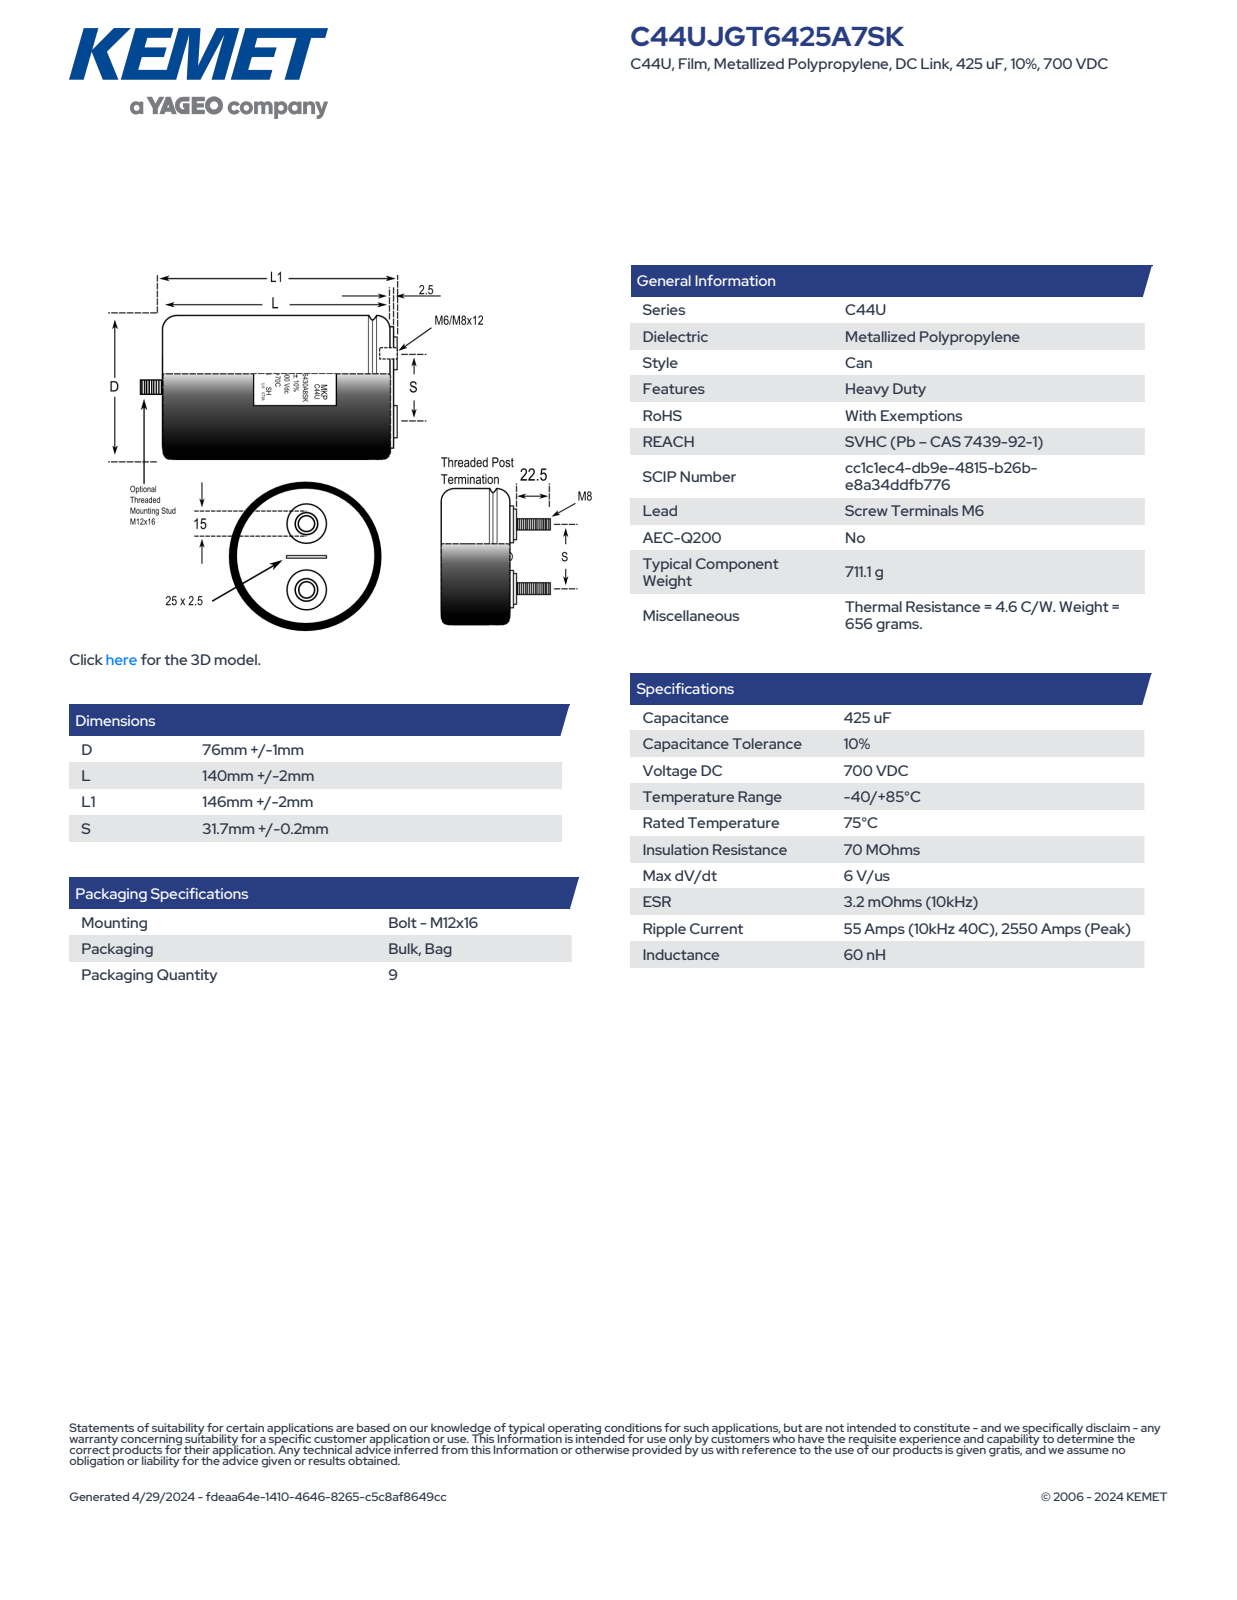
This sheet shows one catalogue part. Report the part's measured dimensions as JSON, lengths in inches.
{"part_name": "CFP_C44U_T_76X140_D77L142S31.9", "step_written_by": "SolidWorks 2014 (AUTOMOTIVE_DESIGN)", "units": "inches", "bodies": {"solids": 1, "faces": 104, "planar": 36, "cylindrical": 29, "other": 39}, "overall_size": [6.319, 3.031, 3.031], "volume_in3": 40.13, "surface_area_in2": 67.82, "round_holes": [[0.236, 2]], "round_bosses_or_shafts": [[0.709, 2], [0.591, 2], [3.031, 1], [2.468, 1], [0.472, 1]], "partial_cylinders_radius": [[1.515, 1]], "face_to_face_distances": [5.591, 0.098, 0.049, 5.689, 5.64, 0.63, 6.22, 6.27, 6.319, 6.299], "hole_center_spacings": [1.256]}
